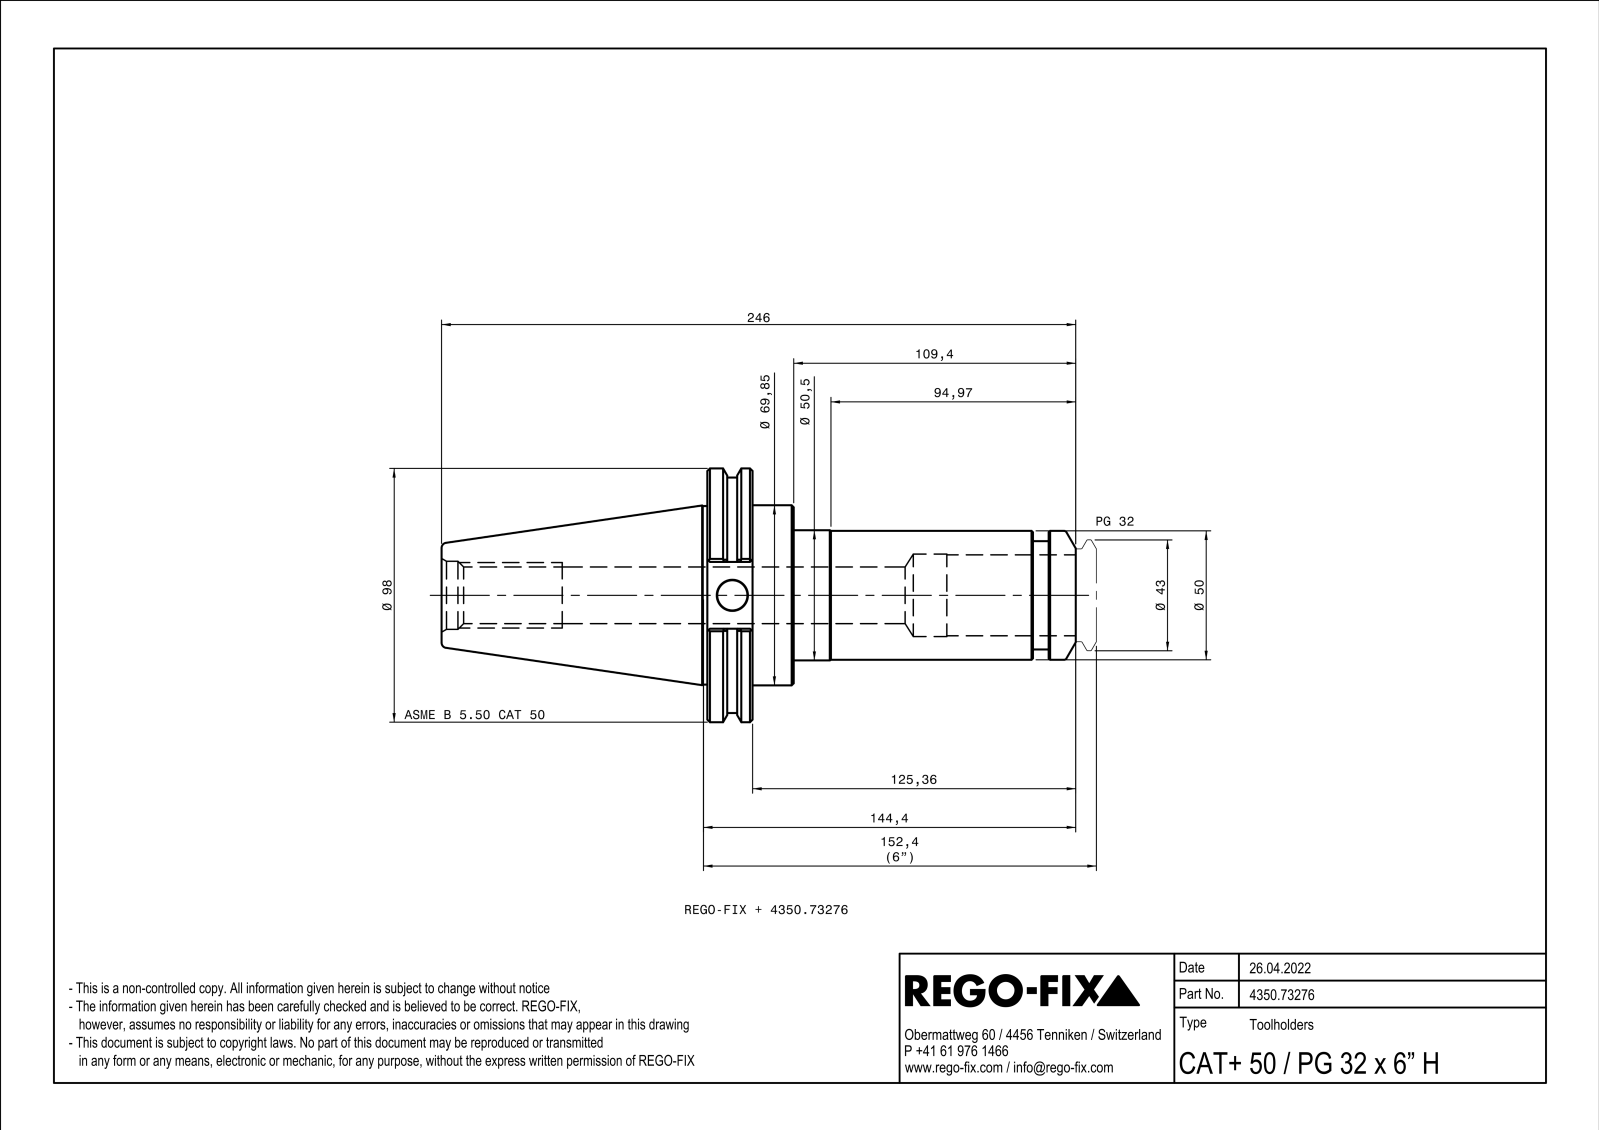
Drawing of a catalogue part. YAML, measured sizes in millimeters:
part_name: "NOCUT"
step_written_by: "SIEMENS PLM Software Solid Edge ST10 (AUTOMOTIVE_DESIGN)"
units: millimeters
bodies: {solids: 2, faces: 262, planar: 108, cylindrical: 59, other: 95}
overall_size: [246.4, 98.72, 94.65]
volume: 1044000
surface_area: 153172
round_holes:
  - {diameter: 3.9, count: 2}
  - {diameter: 4.5, count: 2}
  - {diameter: 3.24, count: 1}
  - {diameter: 12, count: 1}
  - {diameter: 21.96, count: 1}
  - {diameter: 26.1, count: 1}
  - {diameter: 26.4, count: 1}
  - {diameter: 33, count: 1}
round_bosses_or_shafts:
  - {diameter: 98.72, count: 1}
  - {diameter: 98.43, count: 1}
  - {diameter: 91.3, count: 1}
  - {diameter: 70.15, count: 1}
  - {diameter: 69.85, count: 1}
  - {diameter: 69.25, count: 1}
  - {diameter: 50.8, count: 1}
  - {diameter: 50.5, count: 1}
partial_cylinders:
  - {radius: 0.5, count: 4}
face_to_face_distances: [33.75, 17.55, 17.75, 16, 33.55, 16.2, 33.95, 92.55, 92.75, 108.75]
